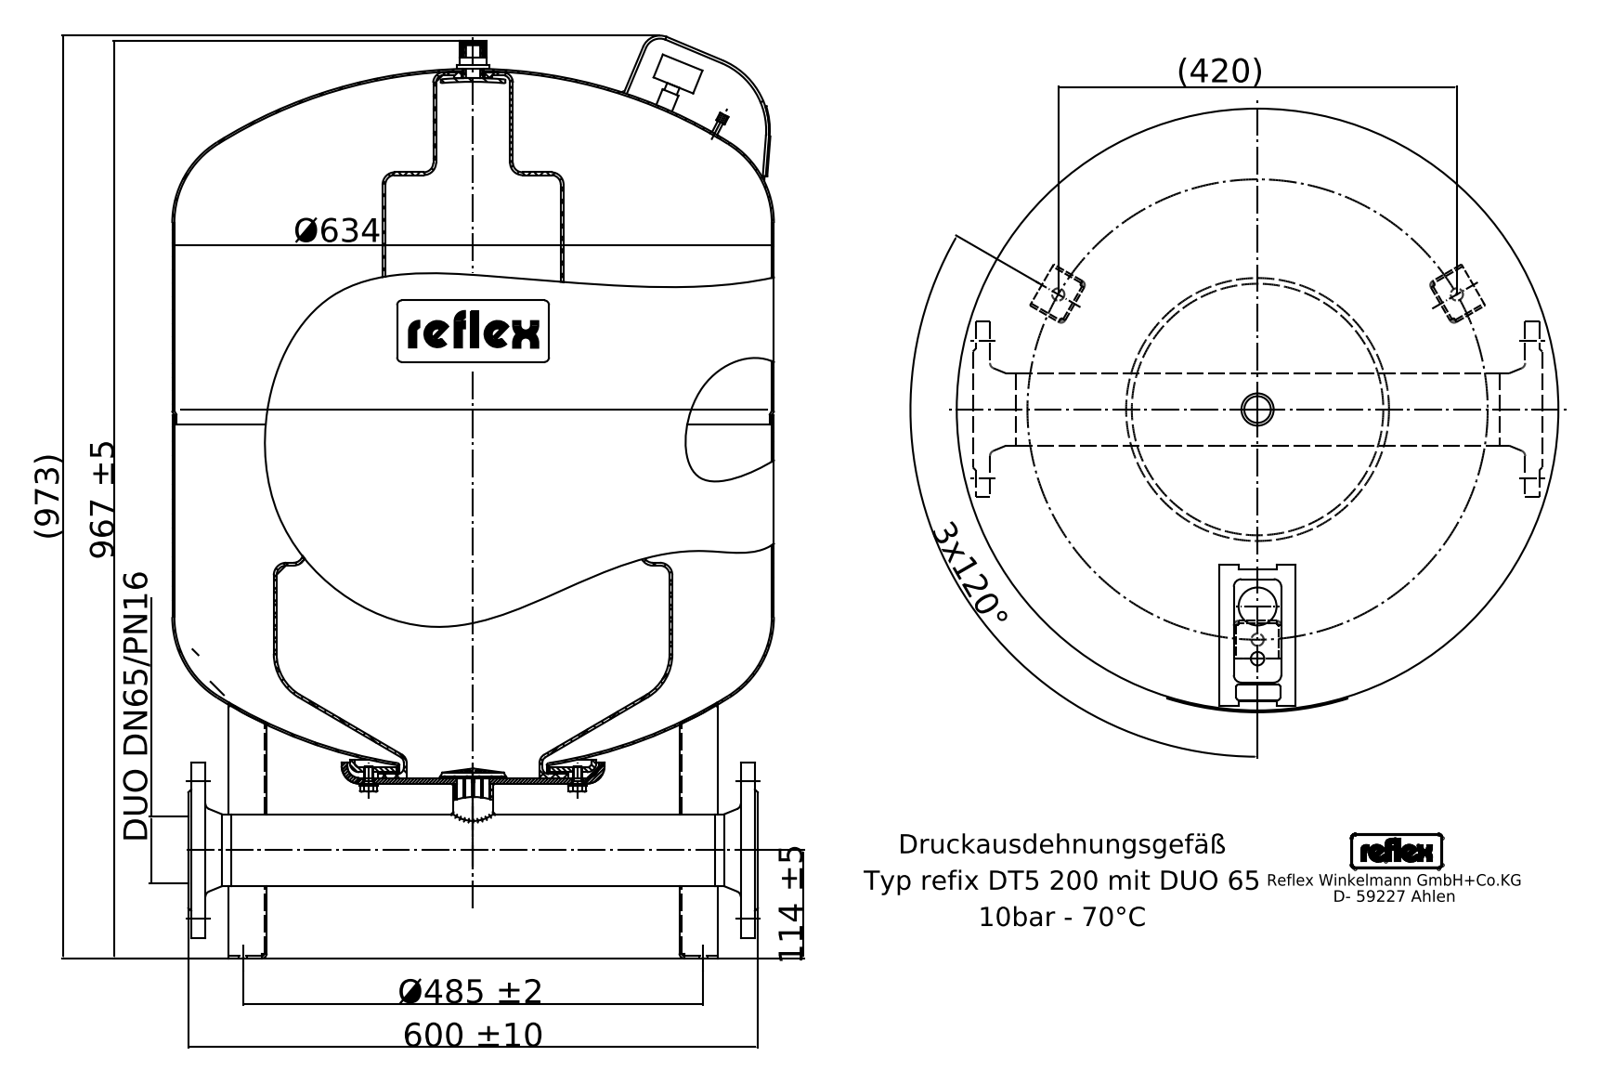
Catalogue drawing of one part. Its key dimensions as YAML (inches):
step_written_by: "Mechanical Desktop 2008 (CONFIG_CONTROL_DESIGN)"
units: inches
bodies: {solids: 23, faces: 521, planar: 223, cylindrical: 185, other: 113}
overall_size: [38.126, 24.961, 24.961]
volume: 12380
surface_area: 5809
round_holes:
  - {diameter: 0.748, count: 4}
  - {diameter: 0.528, count: 3}
  - {diameter: 0.098, count: 1}
  - {diameter: 0.15, count: 1}
  - {diameter: 0.169, count: 1}
  - {diameter: 0.173, count: 1}
  - {diameter: 0.215, count: 1}
  - {diameter: 0.276, count: 1}
  - {diameter: 0.315, count: 1}
  - {diameter: 0.449, count: 1}
  - {diameter: 2.996, count: 1}
  - {diameter: 6.181, count: 1}
round_bosses_or_shafts:
  - {diameter: 0.394, count: 9}
  - {diameter: 24.961, count: 1}
  - {diameter: 10.236, count: 1}
  - {diameter: 9.055, count: 1}
  - {diameter: 7.283, count: 1}
  - {diameter: 2.441, count: 1}
  - {diameter: 1.669, count: 1}
  - {diameter: 1.339, count: 1}
partial_cylinders:
  - {radius: 0.039, count: 15}
  - {radius: 0.098, count: 15}
  - {radius: 0.197, count: 15}
  - {radius: 0.221, count: 4}
  - {radius: 0.089, count: 3}
  - {radius: 0.151, count: 2}
  - {radius: 0.266, count: 2}
  - {radius: 0.315, count: 2}
face_to_face_distances: [16.378, 0.098, 1.87, 6.654, 23.031, 0.236, 6.89, 23.268, 0.197, 1.969]
hole_center_spacings: [2.855, 4.037, 9.547, 16.536, 5.709]
